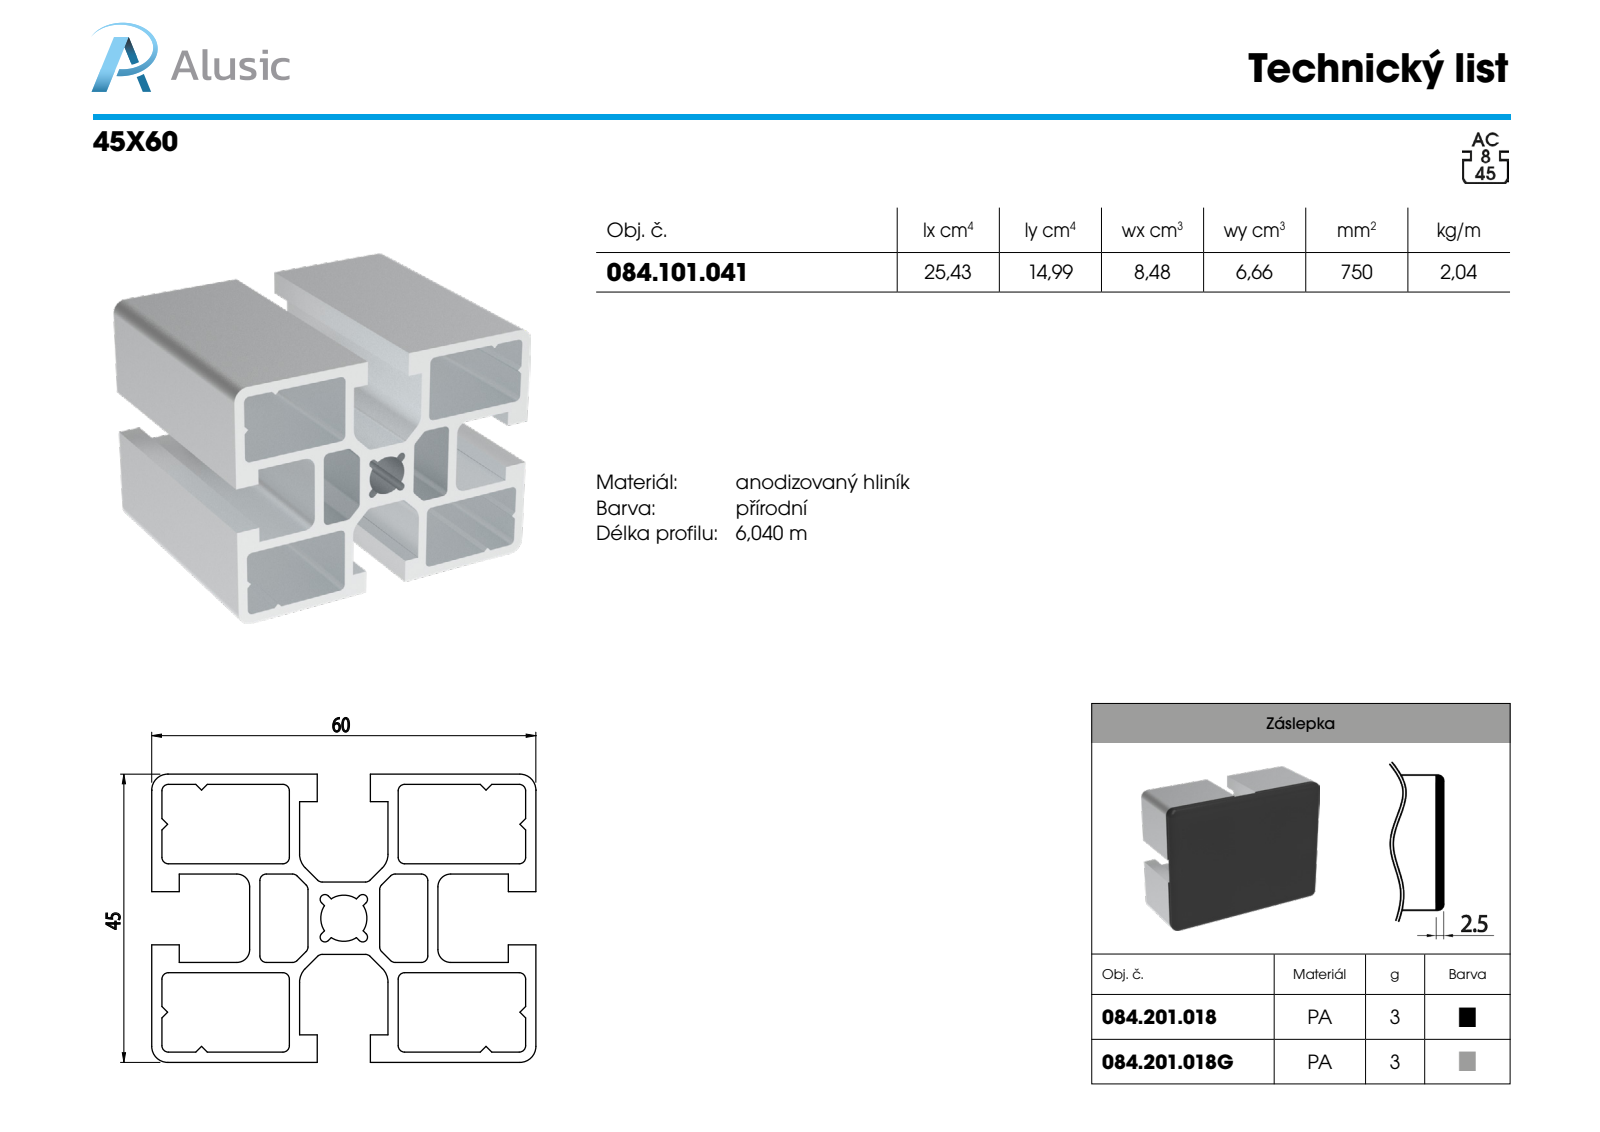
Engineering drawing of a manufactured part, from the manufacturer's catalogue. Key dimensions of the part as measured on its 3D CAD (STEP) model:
Part name (STEP PRODUCT): 084.101.041
STEP written by: SolidWorks 2018 (AUTOMOTIVE_DESIGN)
Units: millimetres
Bodies: 1 solid, 157 faces (102 planar, 55 cylindrical, 0 other)
Overall size (bounding box): 100 × 60 × 45
Volume: 75 144 mm³ · Surface area: 74 102 mm²
Partial cylindrical surfaces — rounded edges, fillets, slot ends (radius × count): R1 ×24, R0.75 ×4, R1 ×4, R1 ×4, R2 ×4, R2.5 ×4, R3.2 ×4, R3.6 ×1
Main face-to-face distances: 1.8, 13.8, 27.6, 13.86, 31.14, 43.2, 12.06, 29.34, 29.4, 38.6
